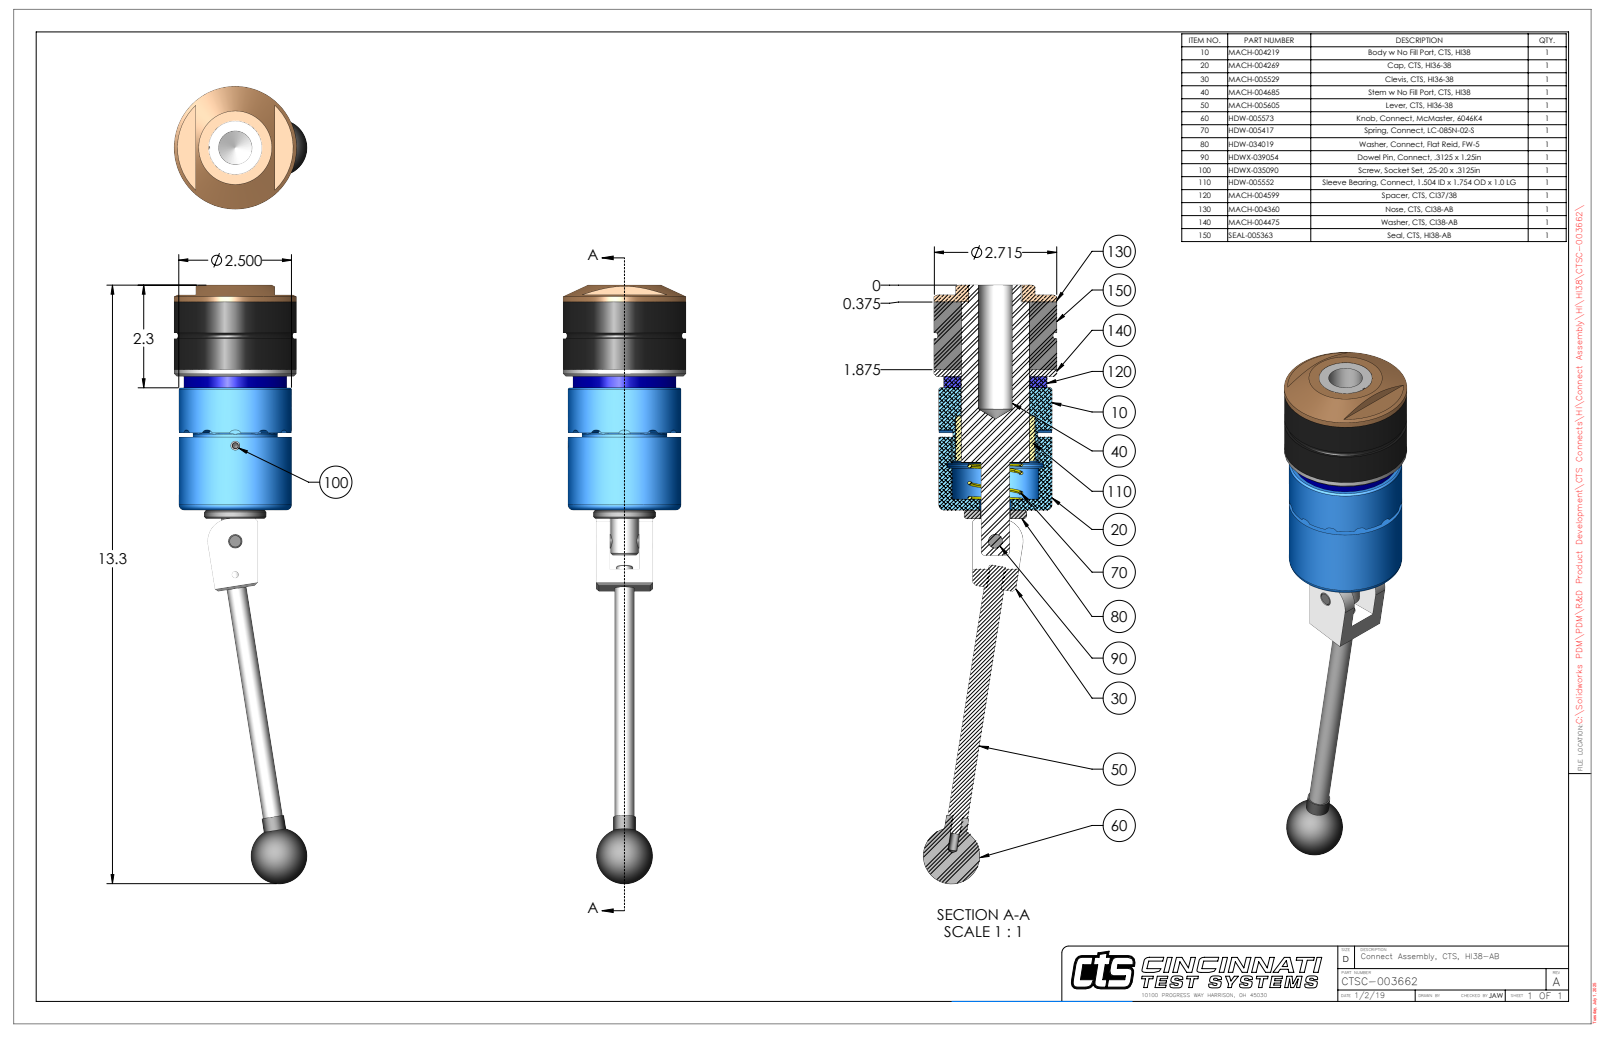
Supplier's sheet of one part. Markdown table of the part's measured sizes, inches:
| quantity | value |
| --- | --- |
| part name | CTSC-003662 |
| STEP written by | SolidWorks 2023 (AUTOMOTIVE_DESIGN) |
| units | inches |
| bodies | 10 solids, 275 faces (98 planar, 108 cylindrical, 69 other) |
| overall size | 13.275 × 2.95 × 2.715 |
| volume | 27.48 in³ |
| surface area | 145.6 in² |
| round holes (diameter × count) | 0.201 × 2, 0.15 × 1, 0.311 × 1, 0.313 × 1, 0.314 × 1, 0.656 × 1, 0.696 × 1, 0.75 × 1, 1.172 × 1, 1.495 × 1, 1.501 × 1, 1.51 × 1 |
| round bosses / shafts (diameter × count) | 2.715 × 1, 2.5 × 1, 2.281 × 1, 1.875 × 1, 1.5 × 1, 1.496 × 1, 1.38 × 1, 1.25 × 1 |
| partial cylindrical surfaces (radius × count) | 0.12 × 12, 0.029 × 2, 0.5 × 1, 1.206 × 1 |
| main face-to-face distances | 1.5, 0.152, 1.652, 0.25, 0.402, 1.902, 2.713, 2.963, 3.115, 4.615 |
| hole center spacings | 0.74, 2.118, 2.858 |
